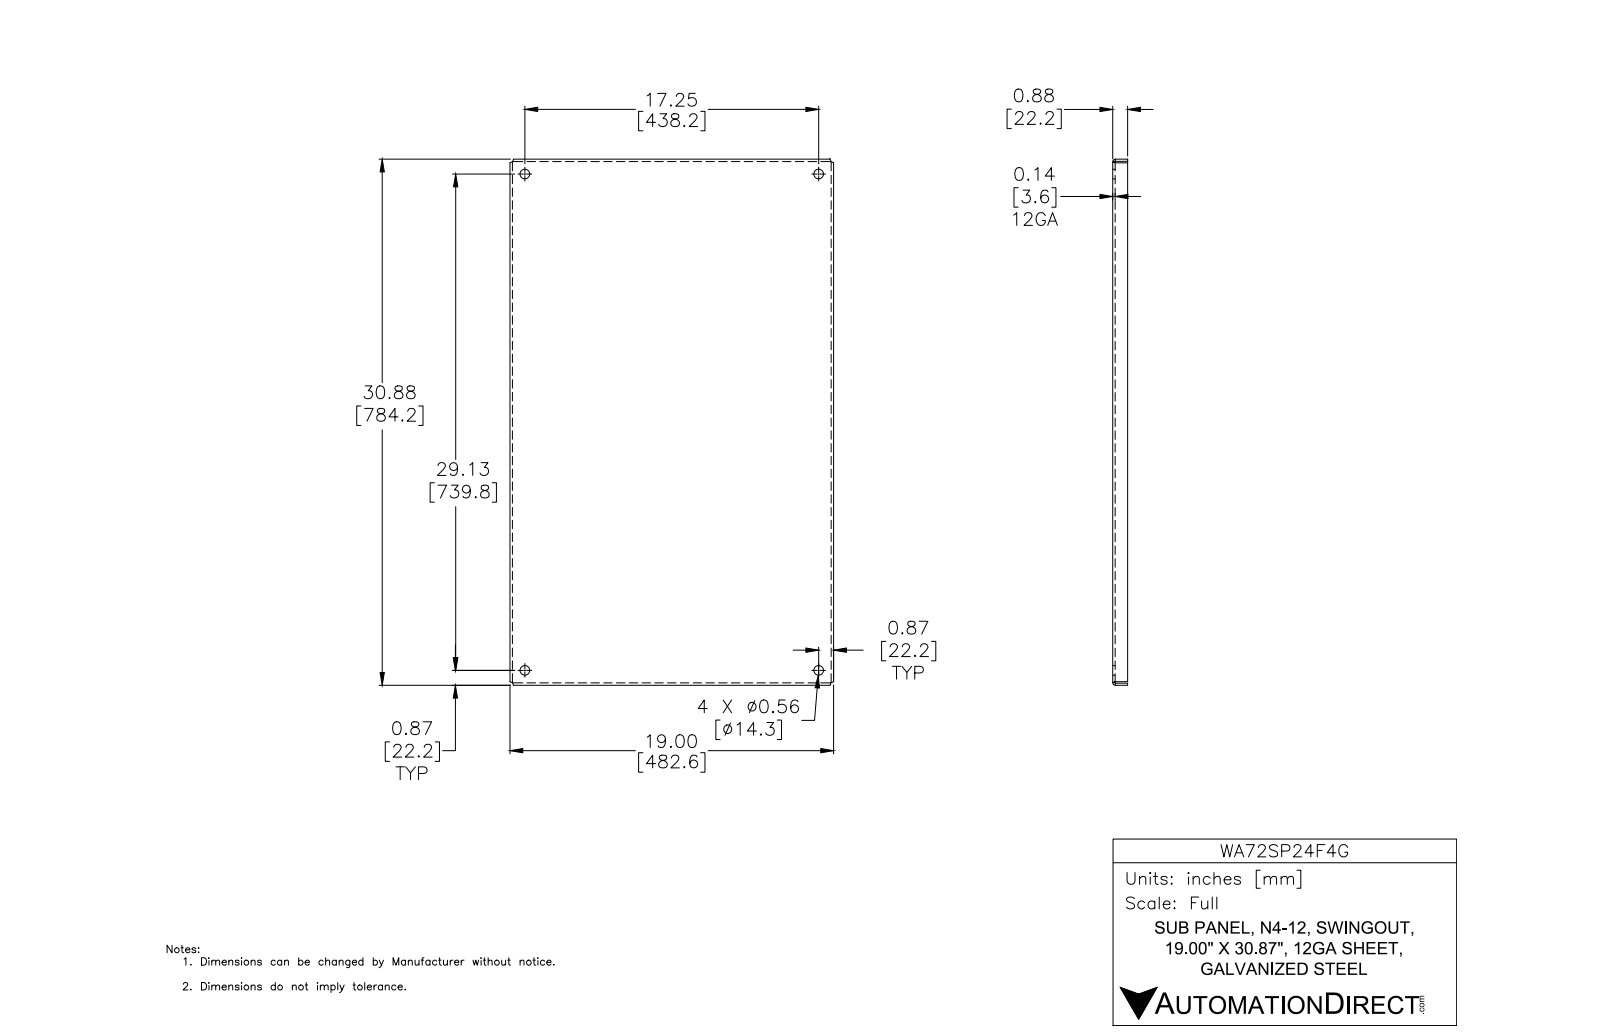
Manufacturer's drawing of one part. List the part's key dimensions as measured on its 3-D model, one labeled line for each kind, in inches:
Part name (STEP PRODUCT): WA60SP24F3G-WA90SP36F4G
STEP written by: Autodesk Inventor 2012 (AUTOMOTIVE_DESIGN)
Units: inches
Bodies: 1 solid, 42 faces (22 planar, 12 cylindrical, 8 other)
Overall size (bounding box): 30.88 × 19 × 0.875
Volume: 61.81 in³ · Surface area: 1 329 in²
Round holes (diameter × count): ⌀0.563 ×4
Partial cylindrical surfaces — rounded edges, fillets, slot ends (radius × count): R0.031 ×4, R0.125 ×4
Main face-to-face distances: 0.094, 18.906, 30.786, 18.813, 19, 30.693, 30.88, 0.781, 0.875, 0.16
Hole centre spacings: 29.13, 33.855, 17.25, 17.25
